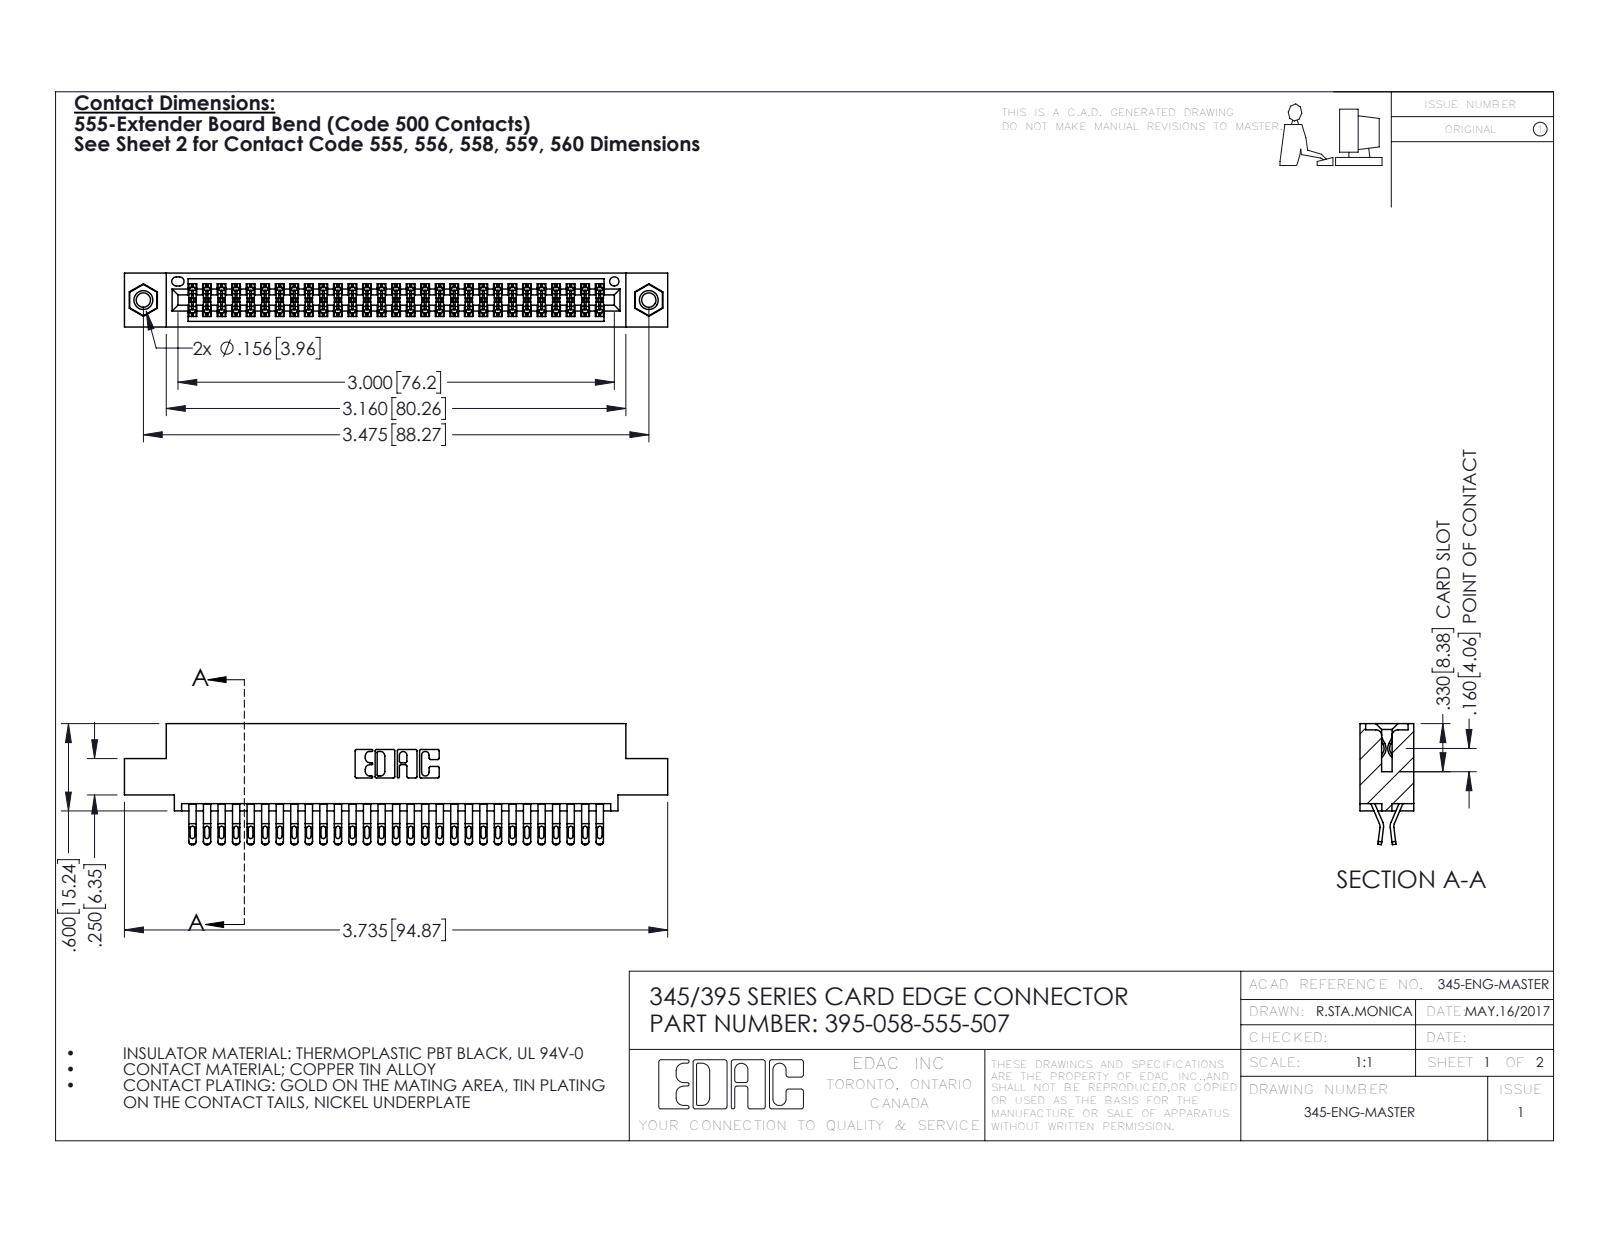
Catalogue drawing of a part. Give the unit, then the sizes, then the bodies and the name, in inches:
Units: inches
Overall size (bounding box): 3.735 × 0.832 × 0.37
Round holes (diameter × count): ⌀0.098 ×2, ⌀0.125 ×2, ⌀0.156 ×2, ⌀0.064 ×1
Round bosses / shafts (diameter × count): ⌀0.155 ×2
Partial cylindrical surfaces — rounded edges, fillets, slot ends (radius × count): R0.016 ×145, R0.02 ×116, R0.006 ×87, R0.01 ×22, R0.007 ×6, R0.031 ×6, R0.026 ×3, R0.01 ×2
Main face-to-face distances: 0.072, 0.298, 0.37, 0.2, 0.025, 0.098, 0.272, 0.225, 0.175, 0.149
Hole centre spacings: 0.27, 3.24, 3.475
Volume: 0.56 in³ · Surface area: 21.73 in²
Bodies: 61 solids, 3438 faces (1914 planar, 1508 cylindrical, 16 other)
Part name (STEP PRODUCT): 345-250-001_345-250-005-103; 345 Part_0.110 Offset - 0.156 Dia-TI; 395-058-555-507; 345-292-001_555 Tail
STEP written by: SolidWorks 2016 (CONFIG_CONTROL_DESIGN)
